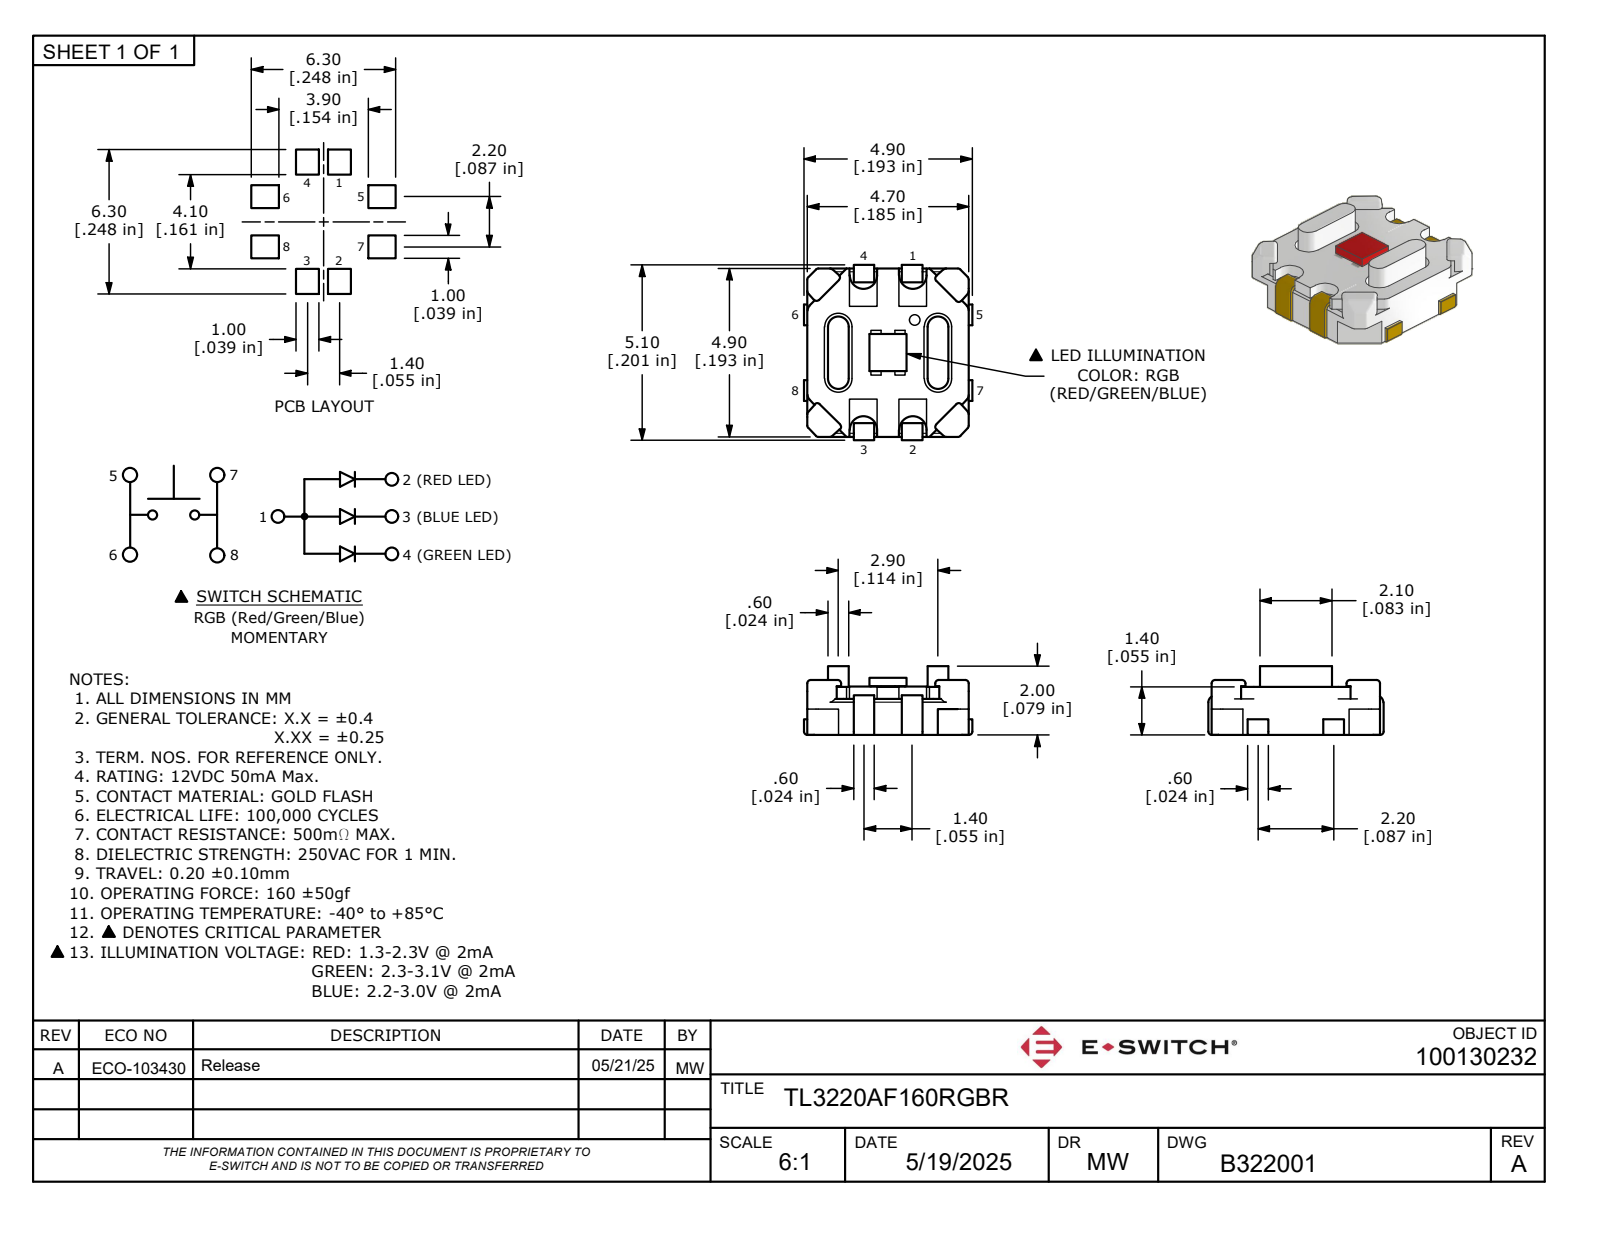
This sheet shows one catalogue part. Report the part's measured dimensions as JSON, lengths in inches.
{"part_name": "100130232_Simplify_1", "step_written_by": "Autodesk Inventor 2022 (AUTOMOTIVE_DESIGN)", "units": "inches", "bodies": {"solids": 1, "faces": 330, "planar": 186, "cylindrical": 108, "other": 36}, "overall_size": [0.201, 0.193, 0.079], "volume_in3": 0.002, "surface_area_in2": 0.151, "round_holes": [[0.012, 3]], "round_bosses_or_shafts": [[0.012, 1]], "partial_cylinders_radius": [[0.004, 62], [0.016, 8], [0.008, 6], [0.012, 4]], "face_to_face_distances": [0.055, 0.024, 0.138, 0.185, 0.114, 0.056, 0.047, 0.028, 0.193, 0.161], "hole_center_spacings": [0.059, 0.118]}
